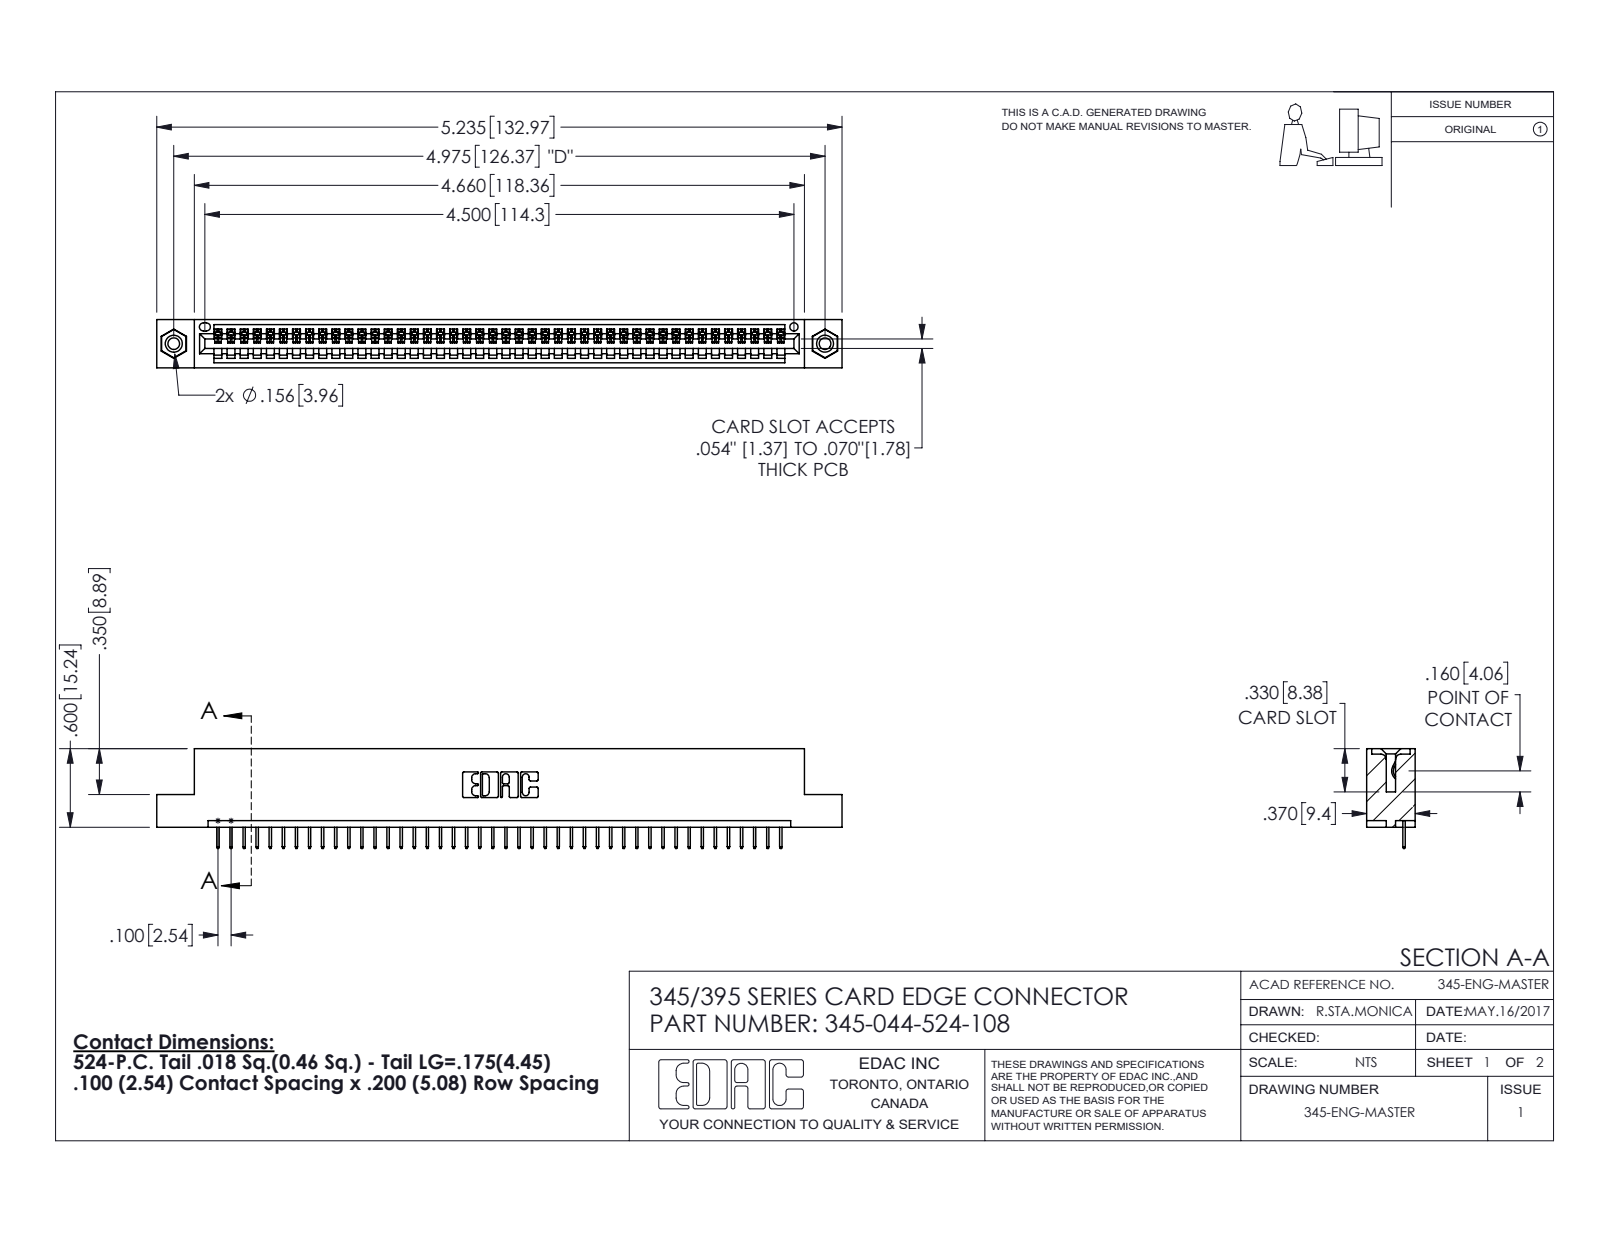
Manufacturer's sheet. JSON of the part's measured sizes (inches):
{"part_name": "345-292-001_345-293-124; 345-250-001_345-250-003-102; 345 Part_Flush Mounting Lugs - 0.156 Dia-TI; 345-044-524-108", "step_written_by": "SolidWorks 2016 (CONFIG_CONTROL_DESIGN)", "units": "inches", "bodies": {"solids": 47, "faces": 2914, "planar": 2136, "cylindrical": 762, "other": 16}, "overall_size": [5.235, 0.762, 0.37], "volume_in3": 0.761, "surface_area_in2": 24.89, "round_holes": [[0.089, 2], [0.125, 2], [0.156, 2], [0.064, 1]], "round_bosses_or_shafts": [[0.155, 2]], "partial_cylinders_radius": [[0.006, 88], [0.01, 22], [0.007, 6], [0.031, 6], [0.026, 3], [0.031, 2], [0.04, 2], [0.014, 1]], "face_to_face_distances": [0.072, 0.298, 0.37, 0.2, 0.098, 0.272, 0.025, 0.225, 0.072, 0.149], "hole_center_spacings": [0.27, 4.739, 4.975]}
